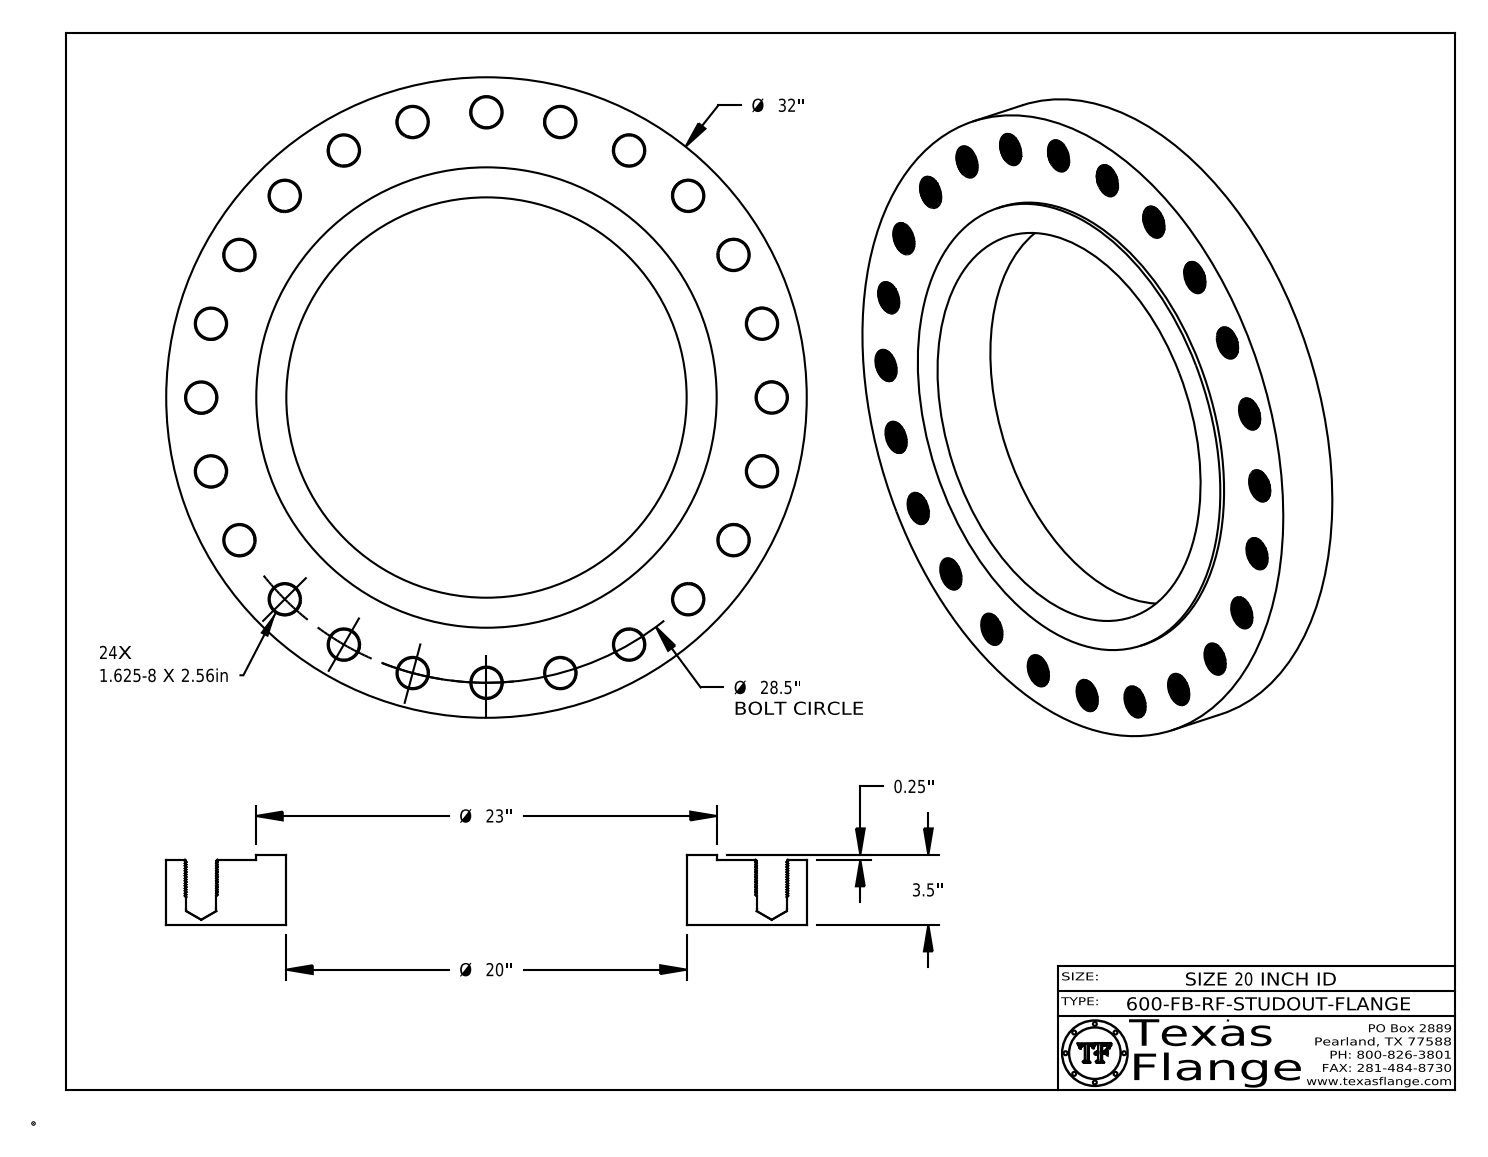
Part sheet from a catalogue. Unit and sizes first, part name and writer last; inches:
Units: inches
Overall size (bounding box): 32 × 32 × 3.5
Round holes (diameter × count): ⌀1.5 ×24, ⌀1 ×1, ⌀20 ×1
Round bosses / shafts (diameter × count): ⌀0.061 ×8, ⌀32 ×1, ⌀23 ×1, ⌀0.788 ×1
Main face-to-face distances: 3.25, 0.25, 3.5, 3.485, 3.235, 0.015, 0.298, 0.293, 0.054, 0.248
Hole centre spacings: 14.25, 3.72, 7.376, 24.682, 26.331, 27.529, 20.153, 10.907
Volume: 1 497 in³ · Surface area: 1 933 in²
Bodies: 1 solid, 2794 faces (368 planar, 794 cylindrical, 1632 other)
Part name (STEP PRODUCT): 20-600-FB-RF-STUDOUT-FLANGE
STEP written by: CATIA V5 STEP AP214 (AUTOMOTIVE_DESIGN)
